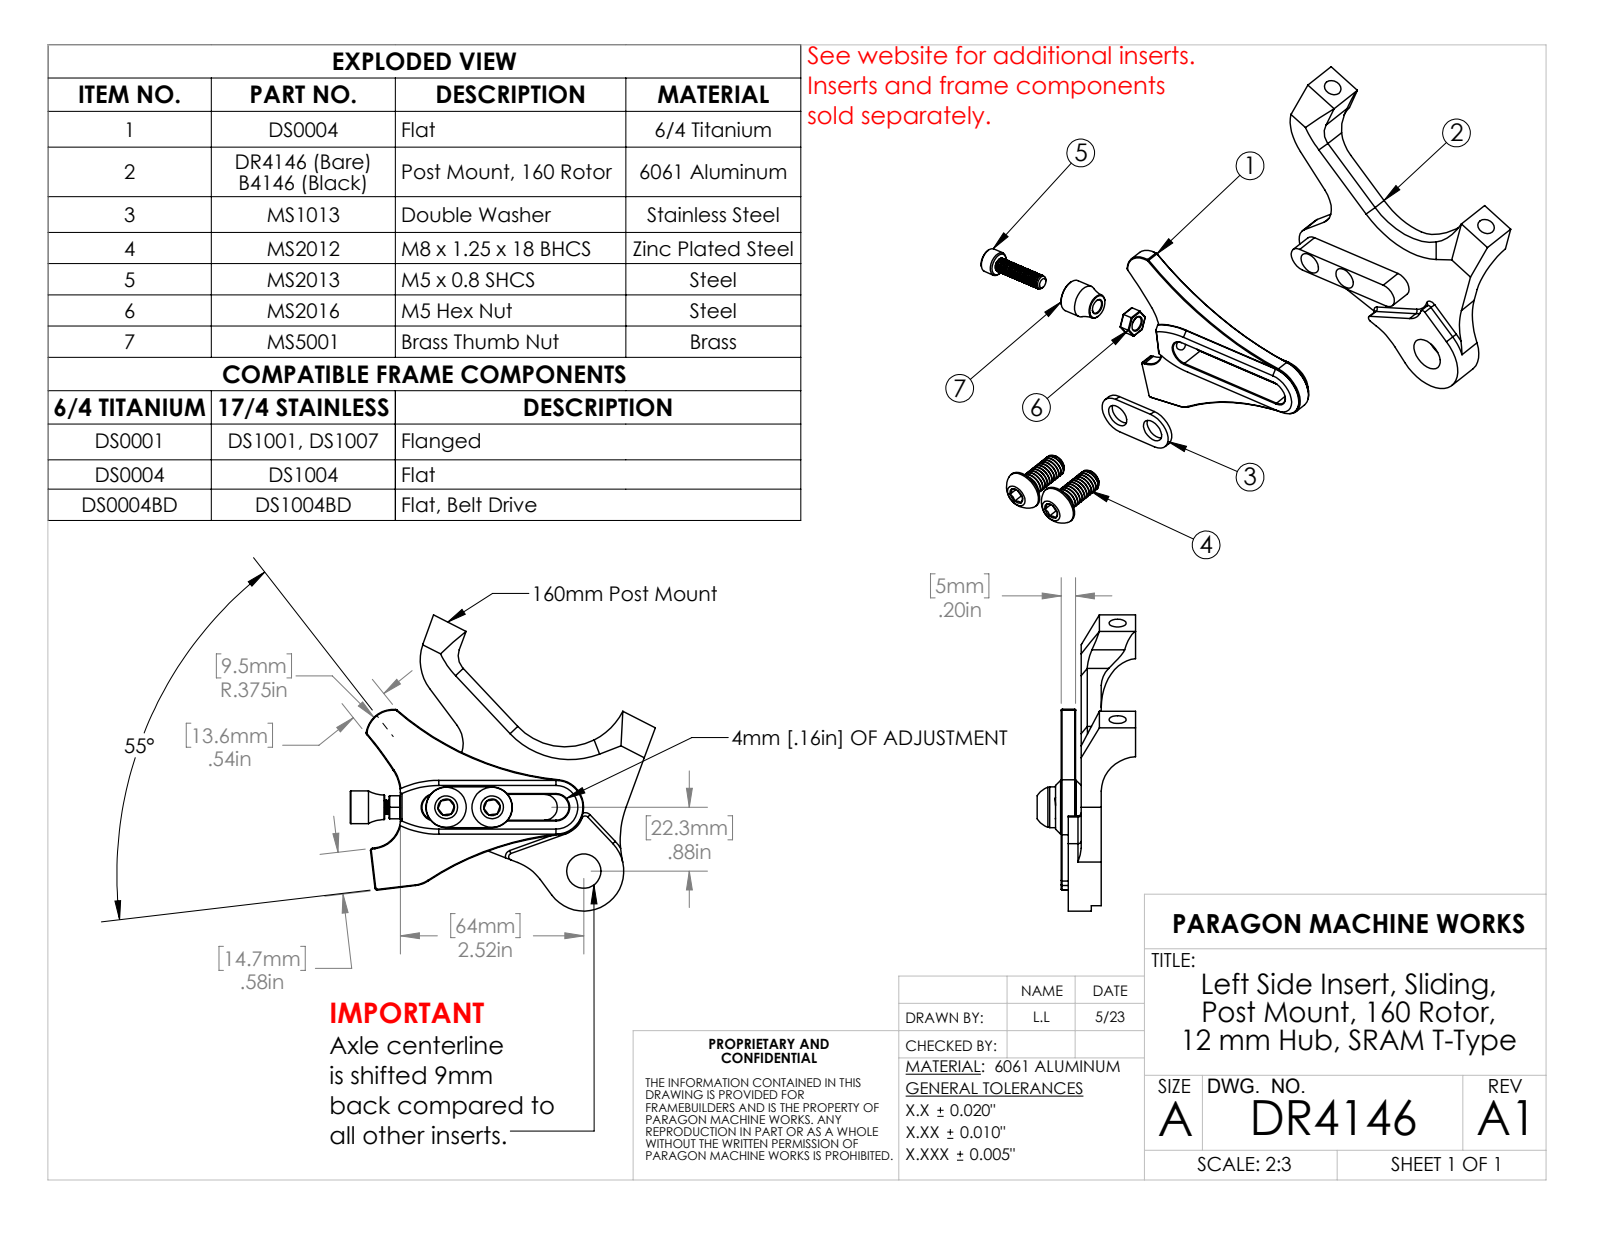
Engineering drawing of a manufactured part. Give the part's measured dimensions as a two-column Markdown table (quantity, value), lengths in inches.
| quantity | value |
| --- | --- |
| part name | 2-HOLE_WASHER; M5x20 SHCS_91292A126; DS0004; 91239A420_Button Head Hex Drive Screw_91239A420 (+4 more) |
| STEP written by | SolidWorks 2022 (AUTOMOTIVE_DESIGN) |
| units | inches |
| bodies | 8 solids, 474 faces (103 planar, 249 cylindrical, 122 other) |
| overall size | 7.354 × 6.693 × 4.071 |
| volume | 3.017 in³ |
| surface area | 38.34 in² |
| round holes (diameter × count) | 0.236 × 2, 0.312 × 2, 0.327 × 2, 0.197 × 1, 0.335 × 1, 0.472 × 1 |
| round bosses / shafts (diameter × count) | 0.551 × 2, 0.315 × 2, 0.449 × 1, 0.197 × 1, 0.156 × 1 |
| partial cylindrical surfaces (radius × count) | 0.01 × 12, 0.03 × 4, 0.045 × 4, 0.178 × 3, 0.5 × 3, 0.28 × 2, 0.39 × 2, 0.4 × 2 |
| main face-to-face distances | 0.276, 0.197, 2.579, 2.855, 2.776, 3.052, 0.079, 0.276, 0.315, 0.356 |
| hole center spacings | 0.63, 1.537, 2.085, 2.921 |
